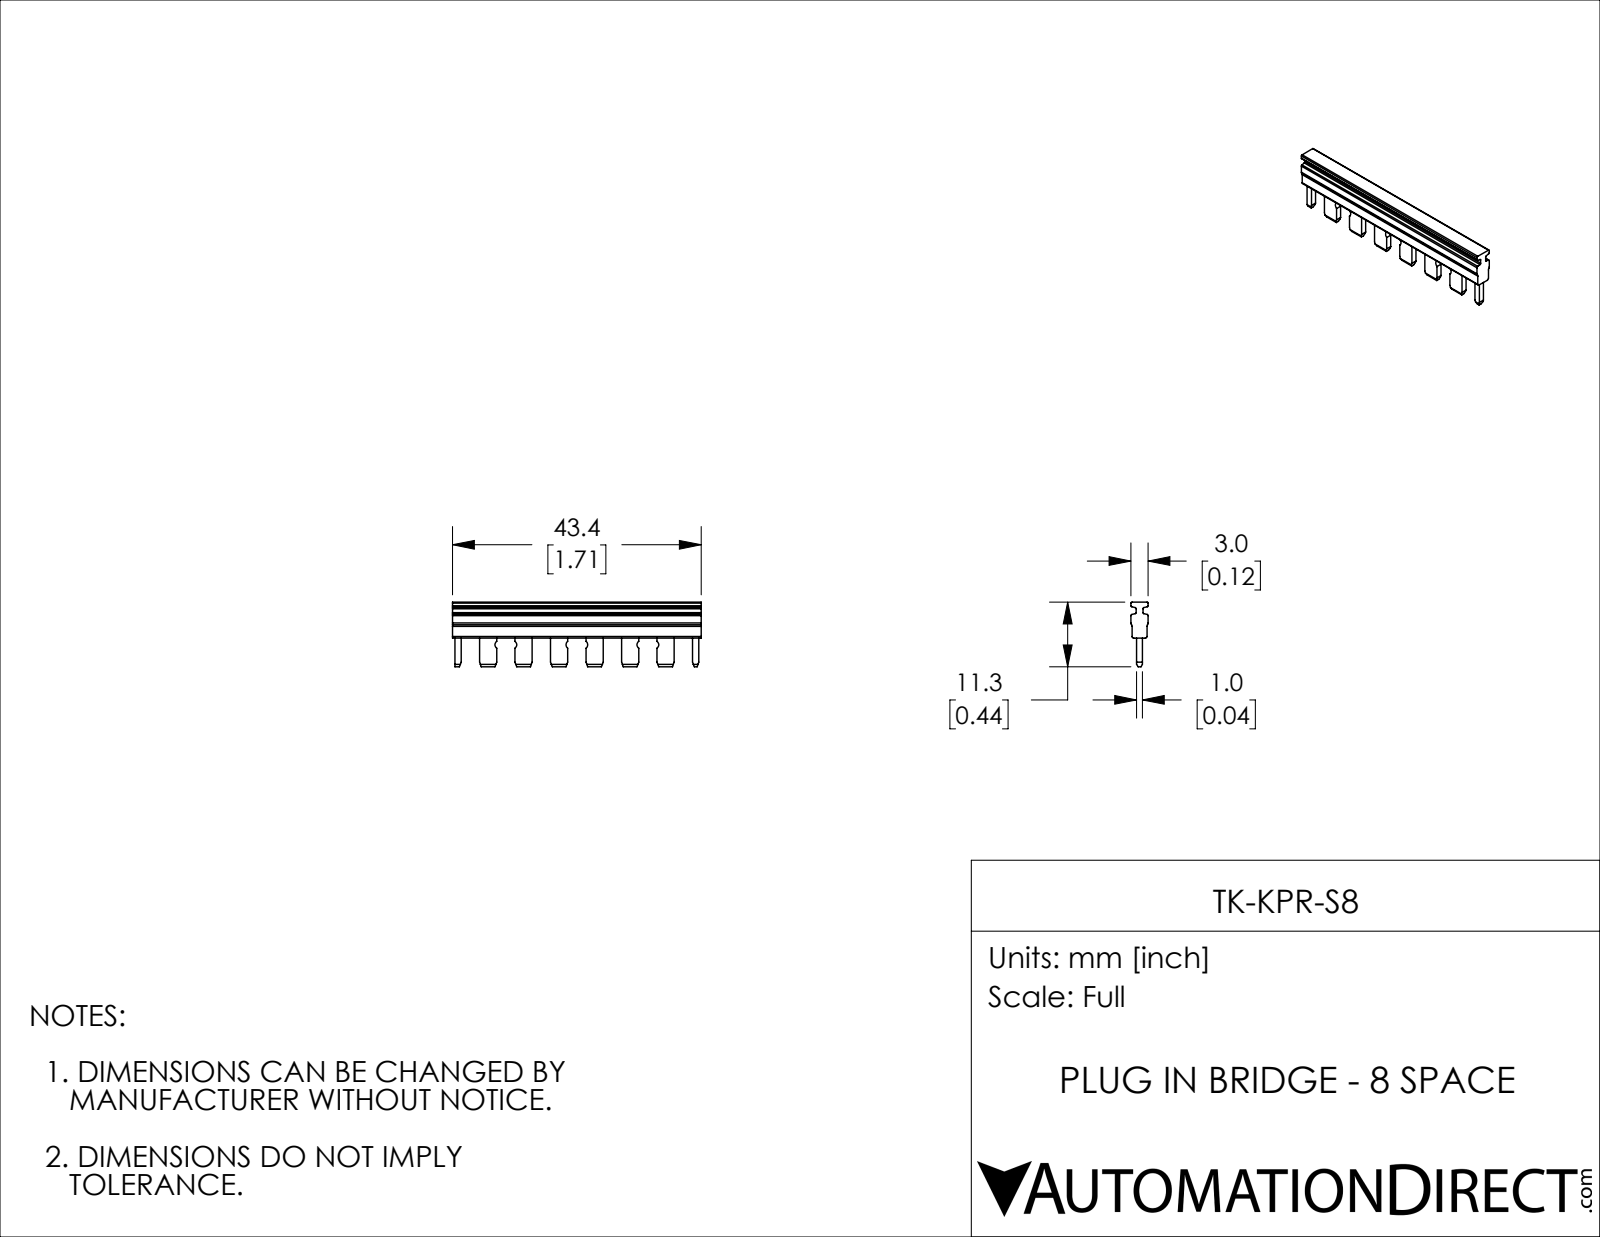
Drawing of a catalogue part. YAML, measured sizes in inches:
part_name: "TK-KPR-S8"
step_written_by: "SolidWorks 2018 (AUTOMOTIVE_DESIGN)"
units: inches
bodies: {solids: 1, faces: 115, planar: 93, cylindrical: 22, other: 0}
overall_size: [1.709, 0.445, 0.118]
volume: 0.048
surface_area: 1.828
partial_cylinders:
  - {radius: 0.008, count: 10}
  - {radius: 0.03, count: 6}
  - {radius: 0.02, count: 4}
  - {radius: 0.012, count: 2}
face_to_face_distances: [0.039, 0.031, 0.071, 0.079, 0.11, 0.118, 0.102, 0.043, 0.248, 0.035]
